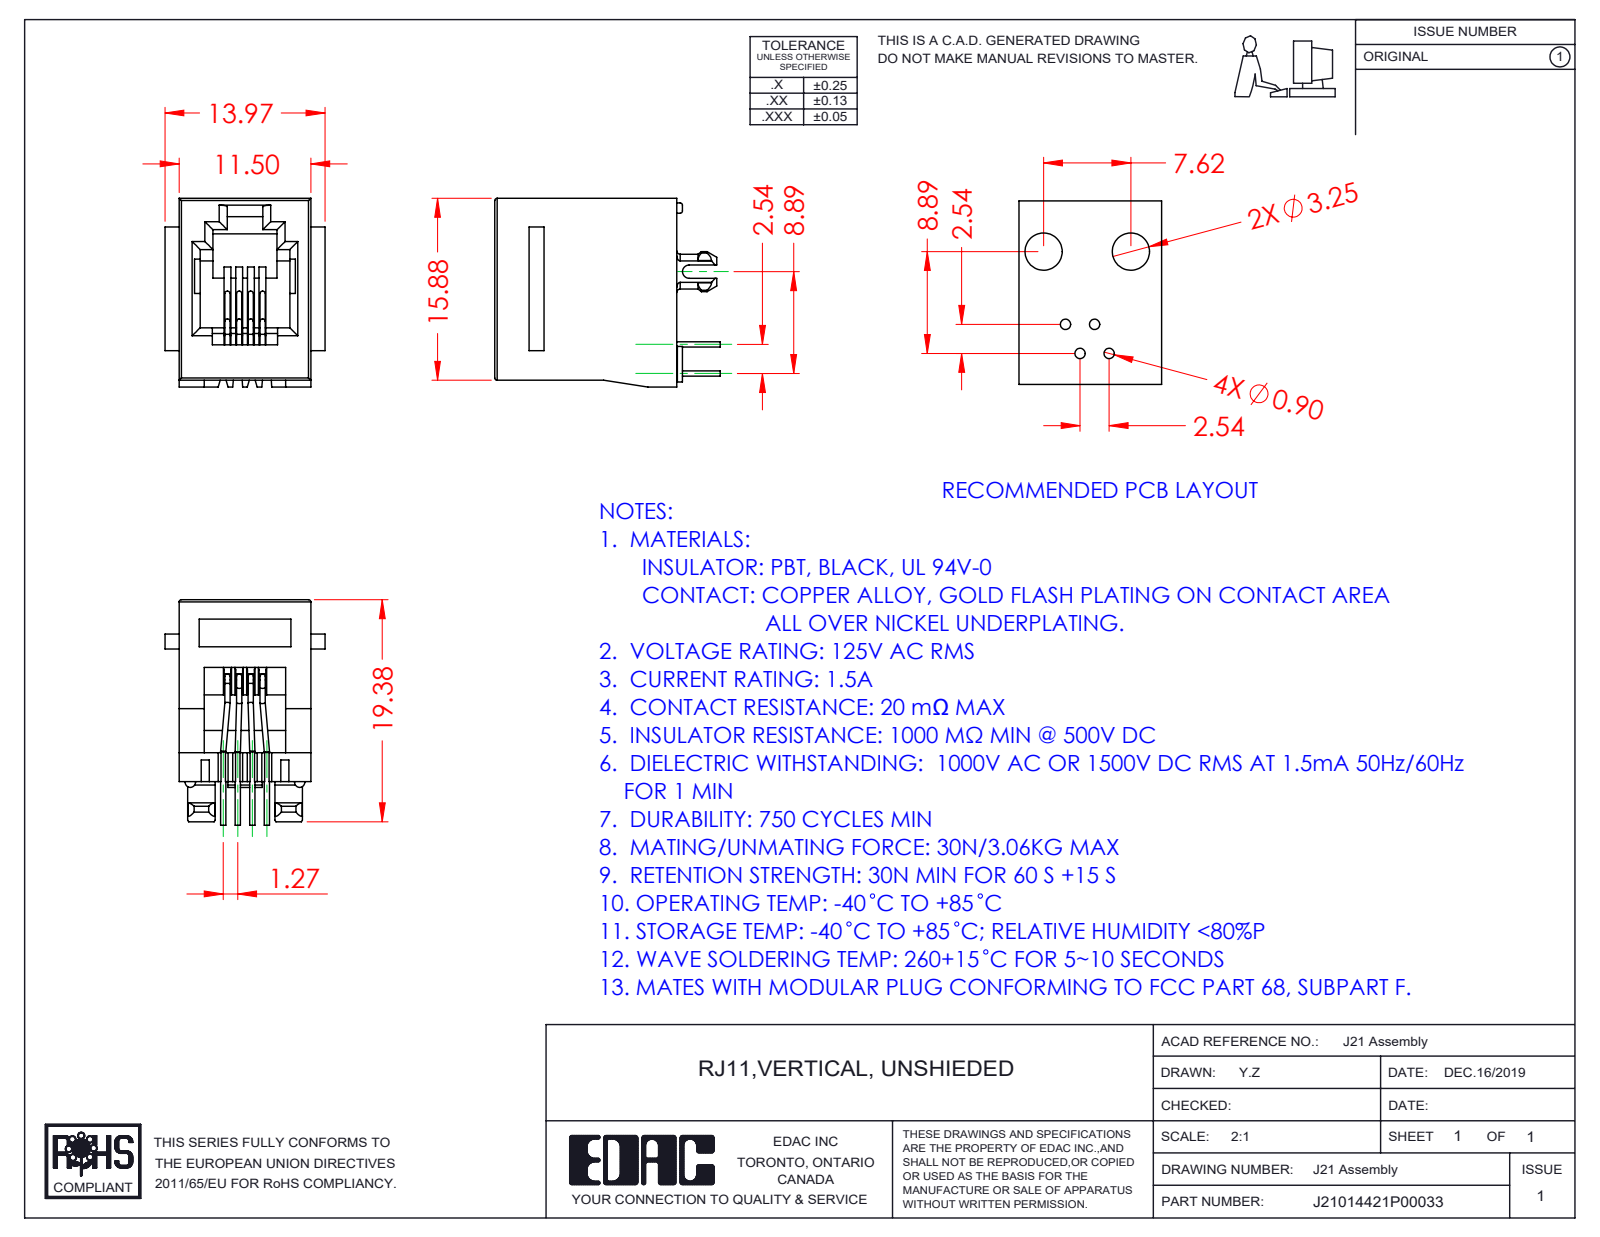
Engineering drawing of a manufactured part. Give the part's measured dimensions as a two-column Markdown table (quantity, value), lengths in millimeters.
| quantity | value |
| --- | --- |
| part name | 21 Insulator; 21 Contacts; RJ21014421P00033 |
| STEP written by | SolidWorks 2016 (CONFIG_CONTROL_DESIGN) |
| units | millimeters |
| bodies | 5 solids, 369 faces (230 planar, 111 cylindrical, 28 other) |
| overall size | 19.68 × 16.48 × 13.97 |
| volume | 1 616 mm³ |
| surface area | 2 564 mm² |
| round holes (diameter × count) | 2 × 2 |
| round bosses / shafts (diameter × count) | 0.46 × 24 |
| partial cylindrical surfaces (radius × count) | 0.5 × 9, 0.7 × 9, 0.2 × 7, 0.23 × 4, 0.45 × 2, 1.52 × 2, 1.75 × 2, 0.57 × 1 |
| main face-to-face distances | 11.5, 1.6, 15.88, 1.02, 7.2, 0.6, 2.95, 8.55, 2.04, 1.35 |
| hole center spacings | 8.4 |
